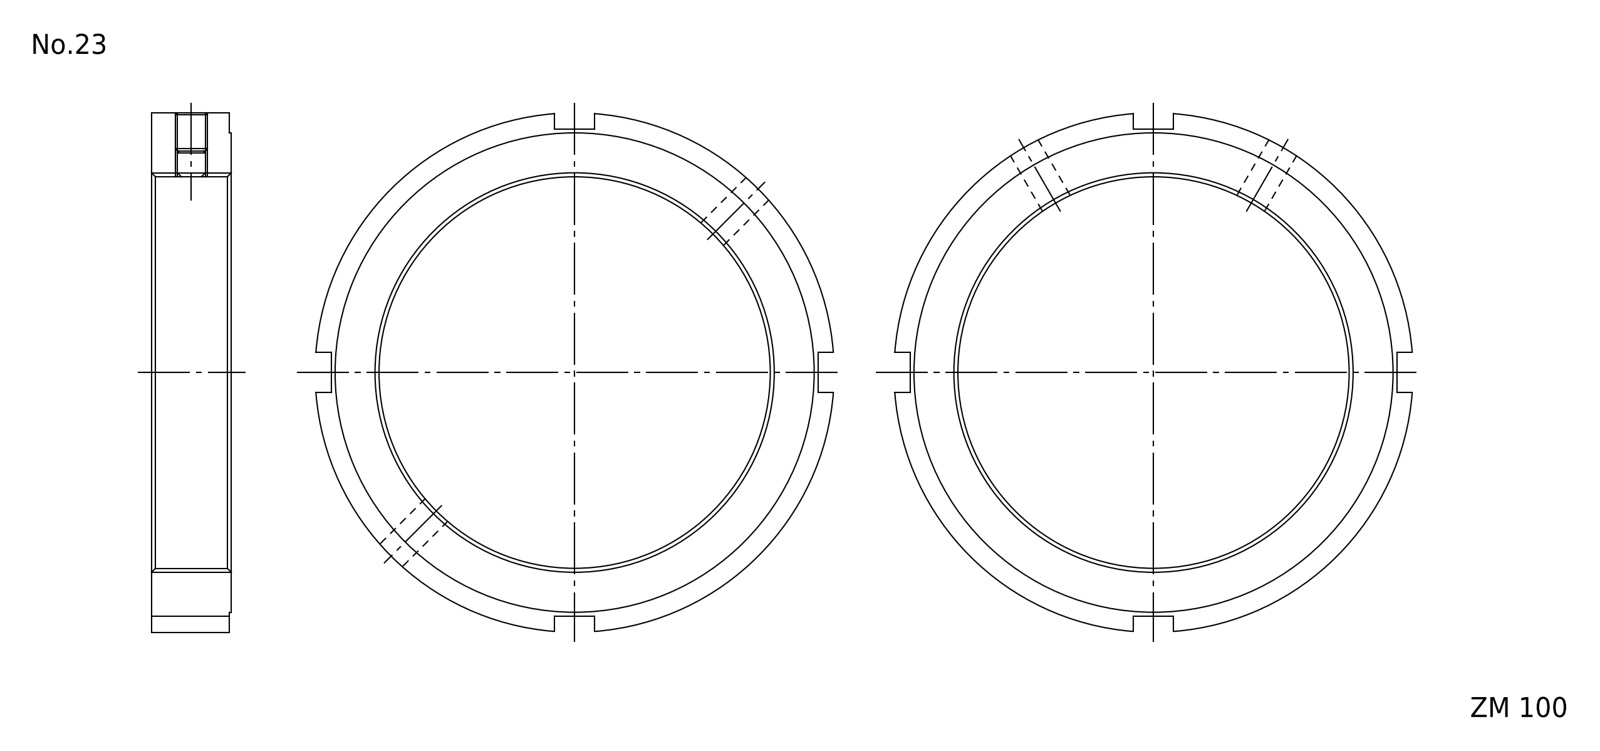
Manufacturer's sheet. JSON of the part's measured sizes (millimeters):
{"part_name": "FKD ZM100", "step_written_by": "Autodesk Inventor 2011 (AUTOMOTIVE_DESIGN)", "units": "millimeters", "bodies": {"solids": 1, "faces": 23, "planar": 15, "cylindrical": 8, "other": 0}, "overall_size": [129.62, 129.62, 20], "volume_mm3": 103292, "surface_area_mm2": 26041, "round_holes": [[6.65, 2], [100, 1]], "round_bosses_or_shafts": [[130, 1], [120, 1]], "face_to_face_distances": [20, 0.5, 19.5, 56, 66, 122, 10]}
